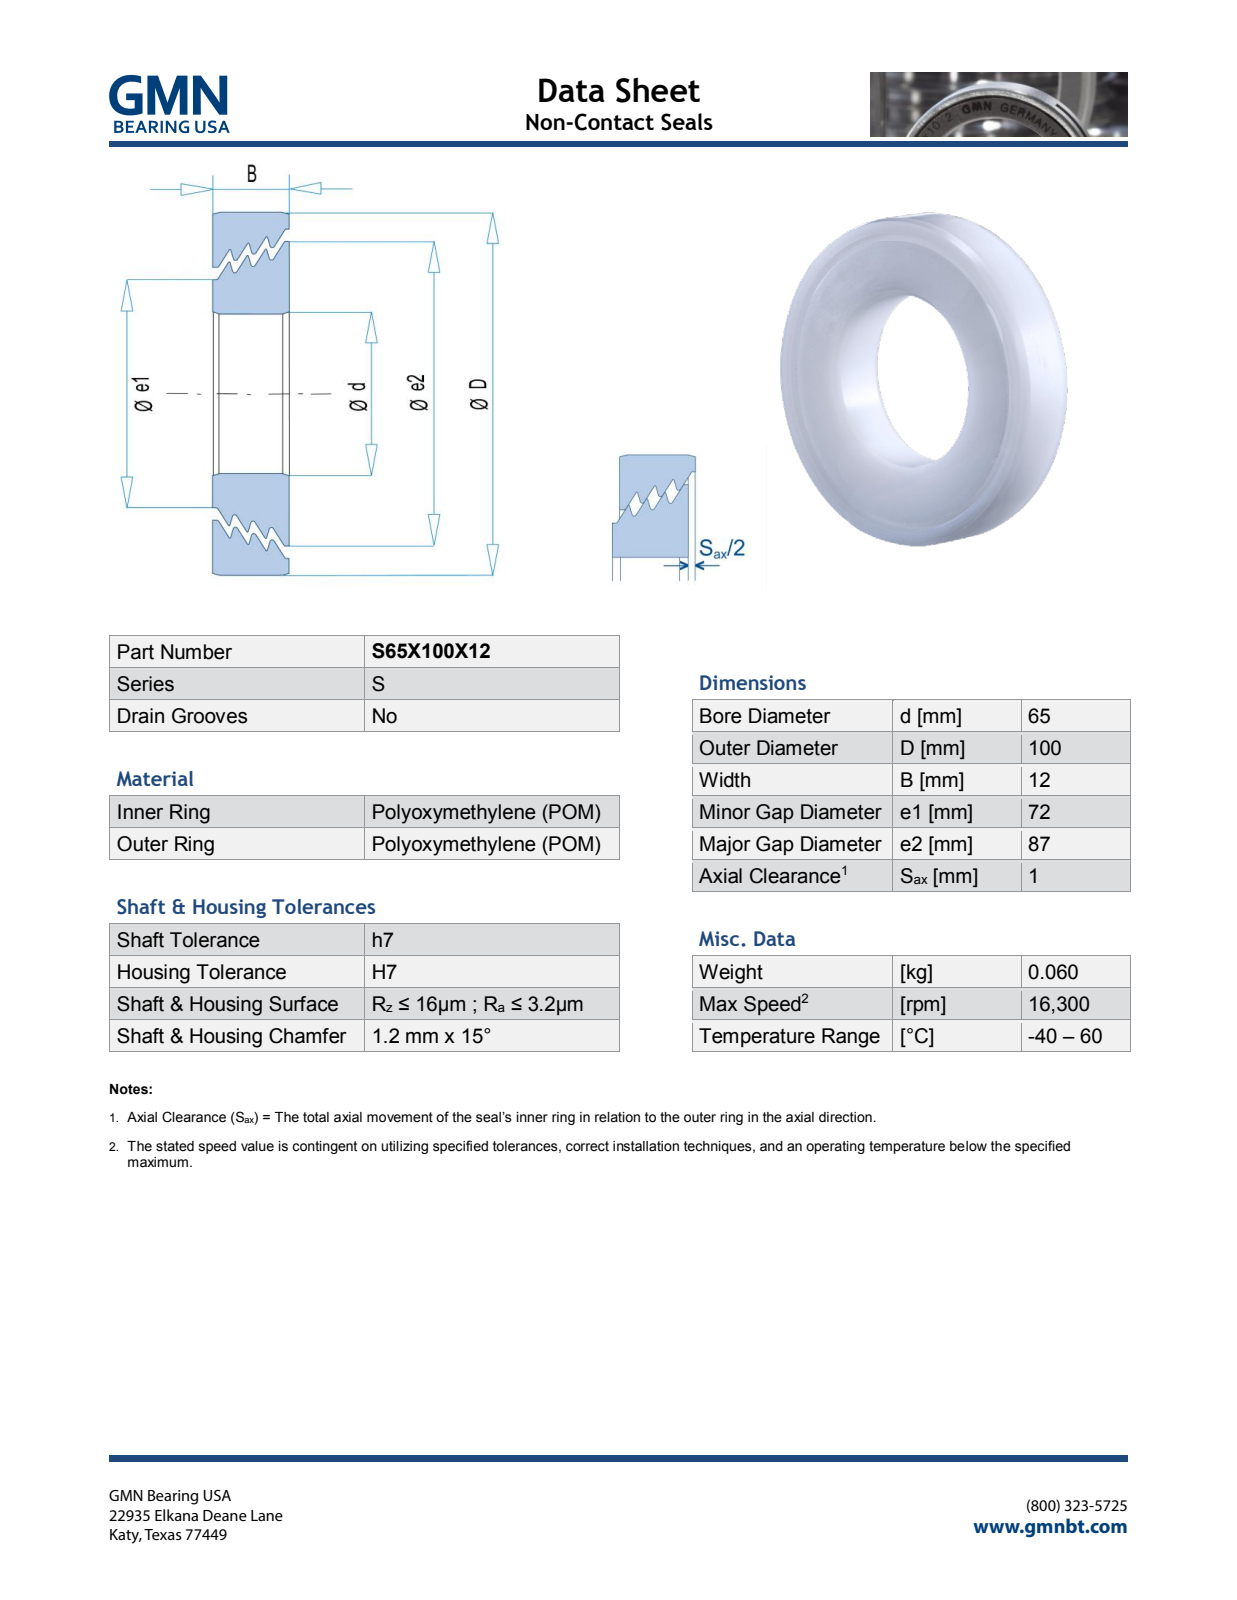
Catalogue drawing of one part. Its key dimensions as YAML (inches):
part_name: "S65X100X12_PRT"
step_written_by: "PRO/ENGINEER BY PARAMETRIC TECHNOLOGY CORPORATION, 2013150 (AUTOMOTIVE_DESIGN)"
units: inches
bodies: {solids: 2, faces: 679, planar: 599, cylindrical: 12, other: 68}
overall_size: [3.937, 3.937, 0.475]
volume: 3.162
surface_area: 42.05
round_holes:
  - {diameter: 2.559, count: 1}
  - {diameter: 2.899, count: 1}
  - {diameter: 3.489, count: 1}
round_bosses_or_shafts:
  - {diameter: 3.937, count: 1}
  - {diameter: 3.425, count: 1}
  - {diameter: 2.835, count: 1}
face_to_face_distances: [0.472, 0.475, 0.015, 0.119, 0.104, 0.015, 0.013, 0.089, 0.013, 0.104]
